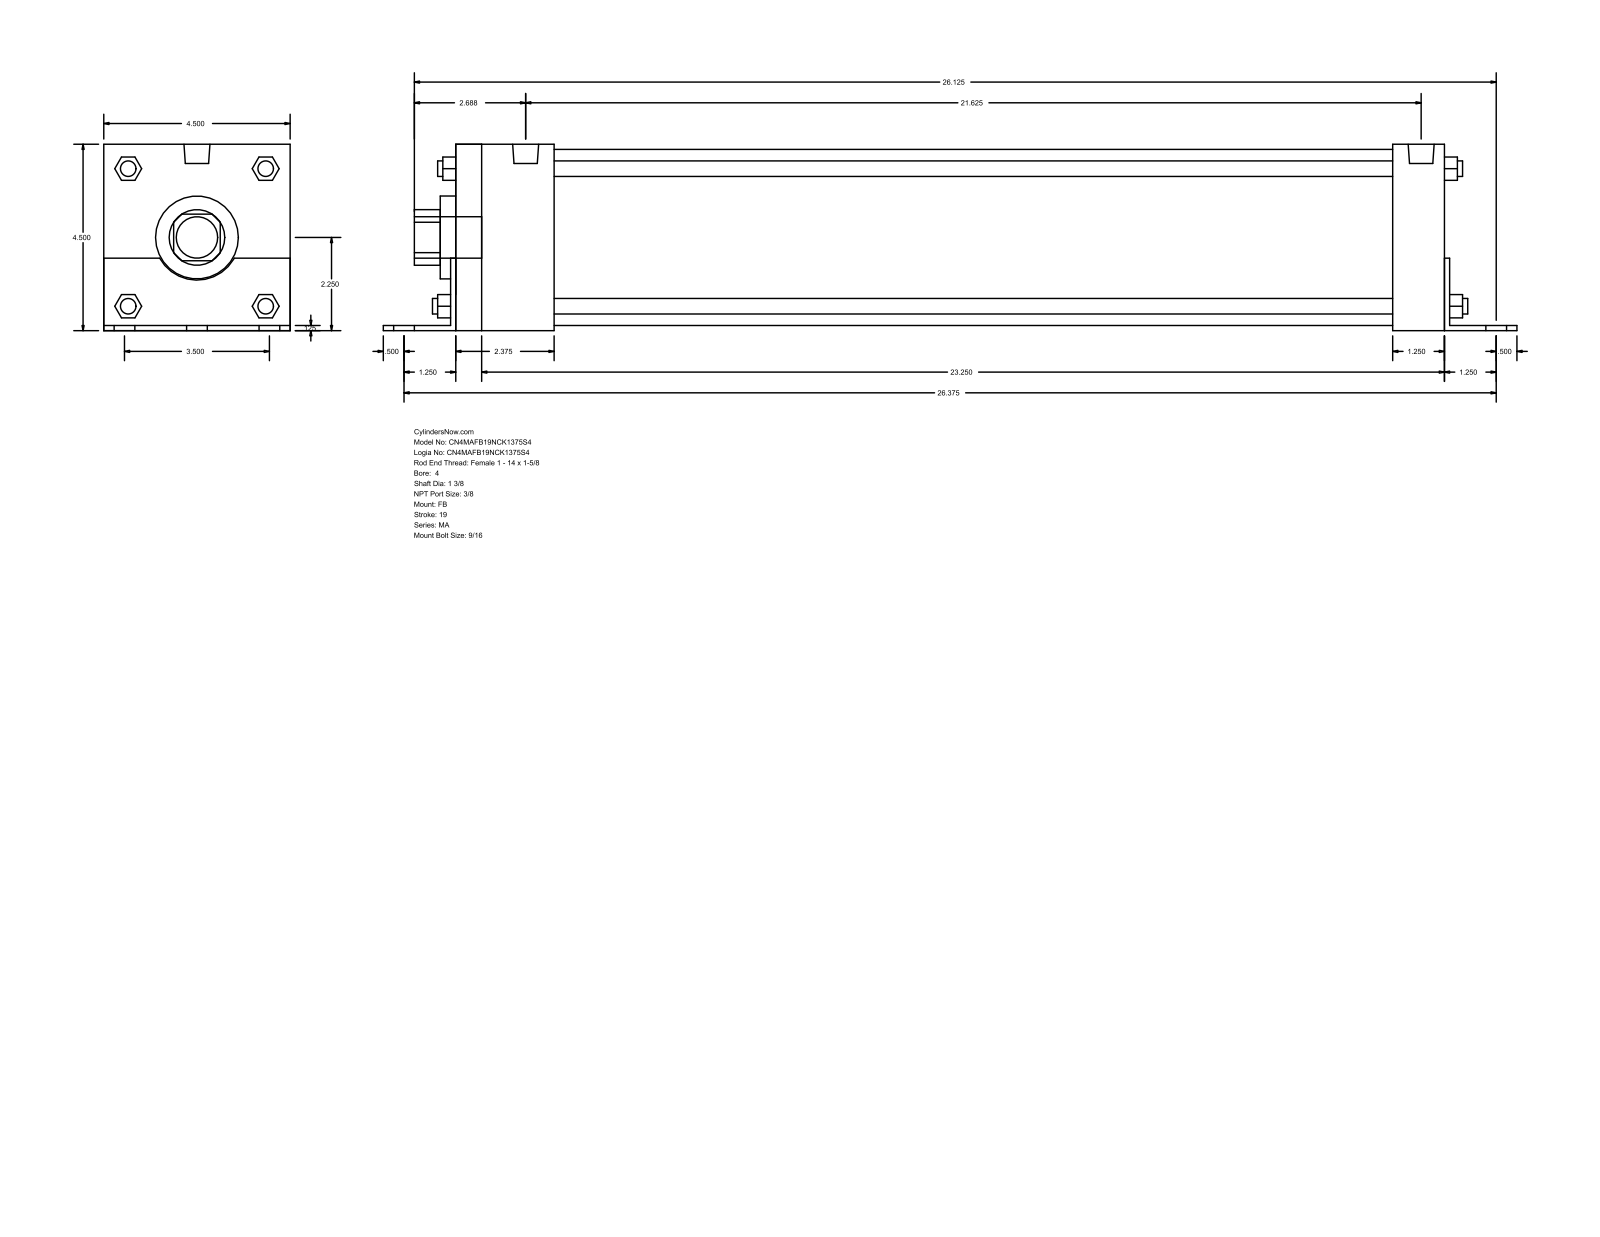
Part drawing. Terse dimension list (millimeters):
name: MA_FB__0400_1.375
written by: GSSL Pune (CONFIG_CONTROL_DESIGN)
unit: mm
bodies: 0 solids, 140 faces (105 planar, 35 cylindrical, 0 other)
size: 695.33 × 114.35 × 114.3
holes: 1× ⌀34.92, 1× ⌀50.8, 1× ⌀107.95
bosses: 6× ⌀14.29, 4× ⌀11.11, 4× ⌀9.53, 2× ⌀15.93, 1× ⌀25.4
rounds: 1× R17.06, 1× R26.16
face distances: 114.3, 3.17, 114.35, 3.12, 111.18, 609.6, 606.43, 60.32, 612.77, 31.75
